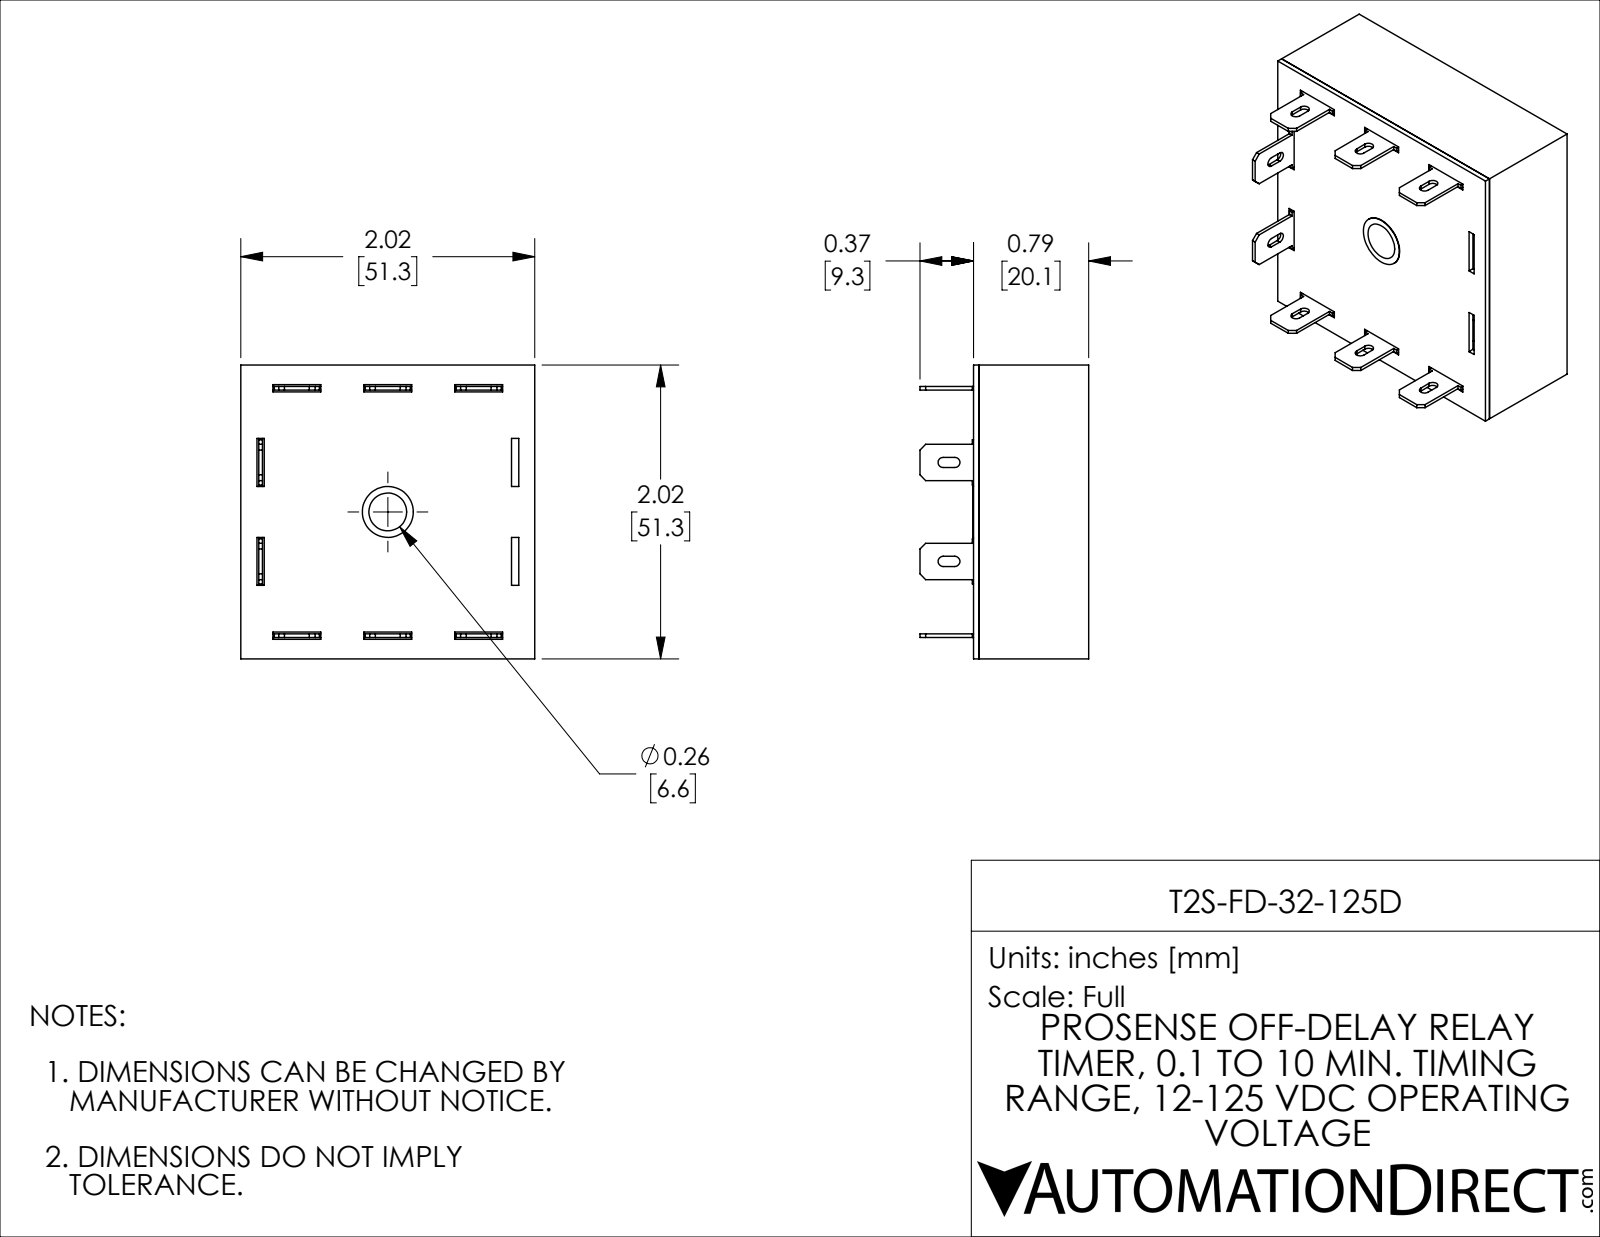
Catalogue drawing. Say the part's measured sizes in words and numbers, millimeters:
The part is named "T2S-FD-32-125D". Its 3-D file was written by "SolidWorks 2021 (CONFIG_CONTROL_DESIGN)". It is 10 solids with 256 faces: 234 planar, 20 cylindrical and 2 other. Overall it measures 51.31 by 51.31 by 29.46 millimeters. Its volume is 11 042 cubic millimeters and its surface area 22 819 square millimeters. Round holes: 1 of diameter 8.89. Partial cylindrical surfaces (rounded edges, fillets, slot ends): 10 of radius 0.89. The main face-to-face distances are 1.14, 50.16, 19.15, 20.12, 0.97, 18.01, 18.98, 51.3, 49.02, 3.74.
